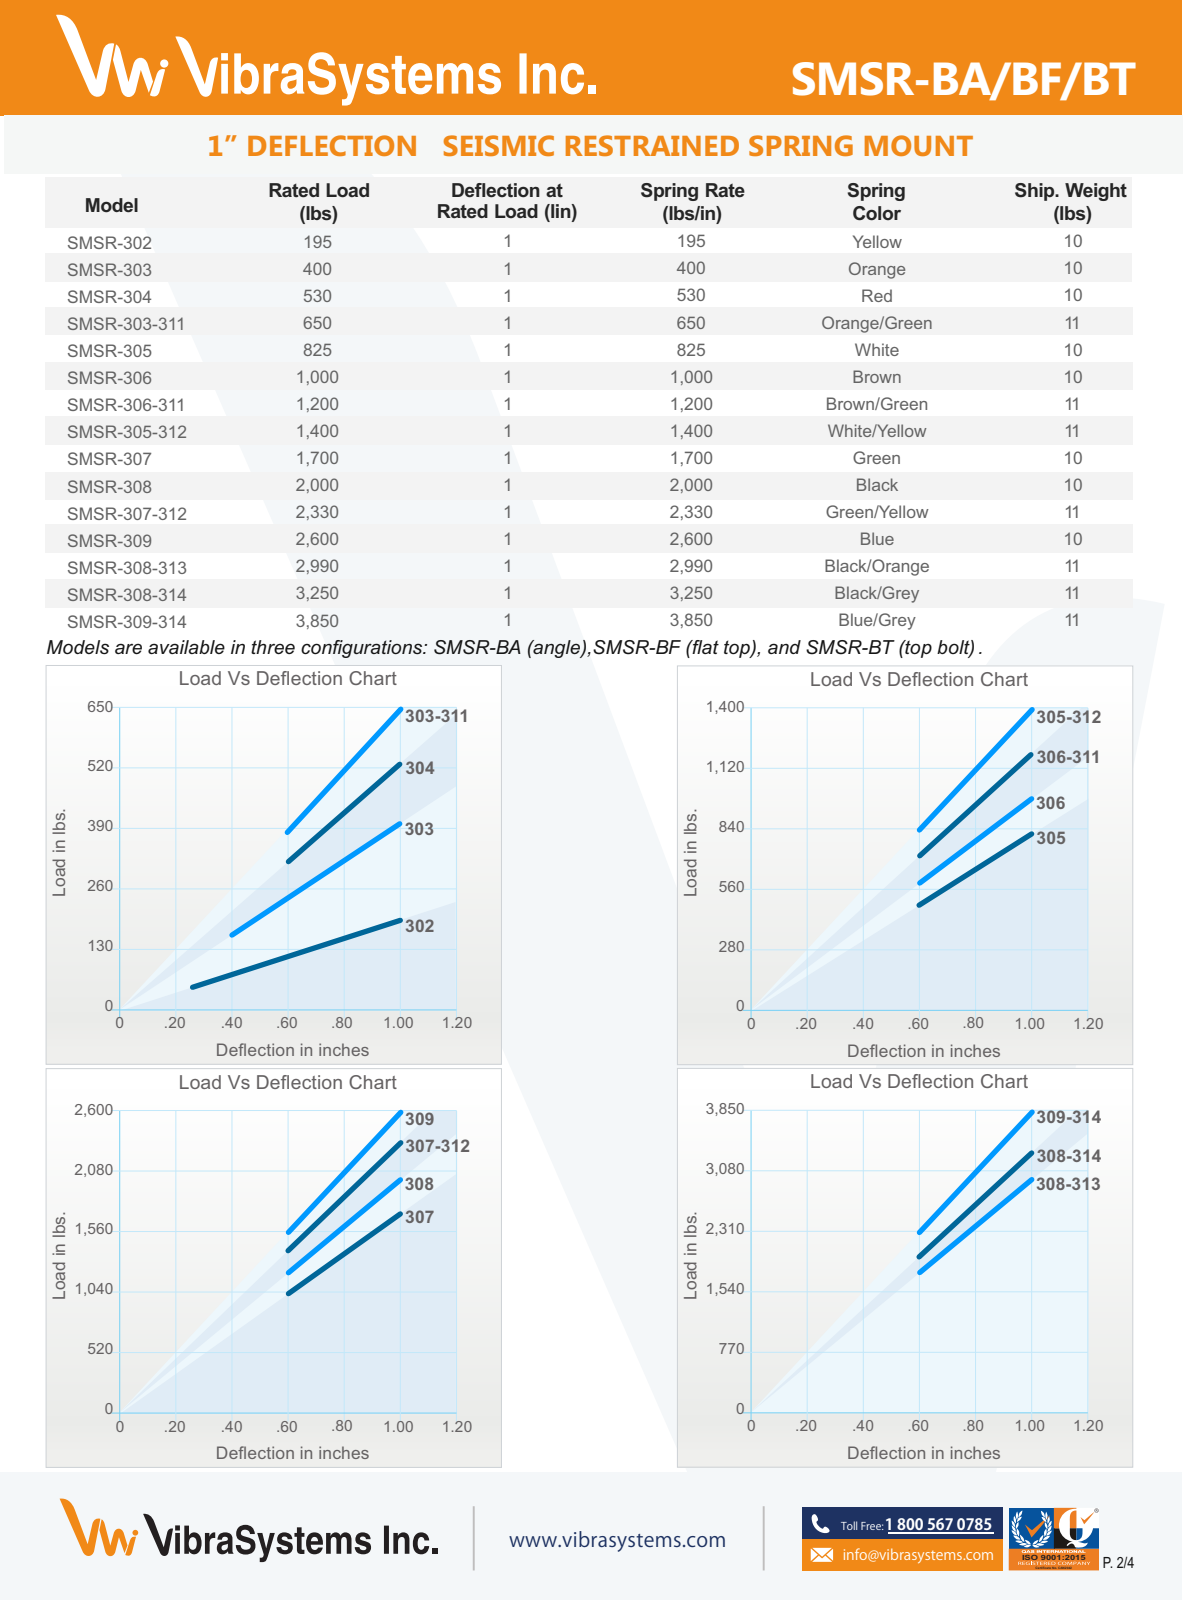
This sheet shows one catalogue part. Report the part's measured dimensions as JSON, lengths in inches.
{"part_name": "SMSR-BA Rev M", "step_written_by": "SolidWorks 2016 (CONFIG_CONTROL_DESIGN)", "units": "inches", "bodies": {"solids": 1, "faces": 121, "planar": 61, "cylindrical": 52, "other": 8}, "overall_size": [10.5, 7.5, 3.875], "volume_in3": 69.75, "surface_area_in2": 282.5, "round_holes": [[0.687, 3]], "round_bosses_or_shafts": [[0.5, 3], [1.5, 2], [1.4, 2], [3.5, 1], [3, 1], [1.375, 1]], "partial_cylinders_radius": [[0.25, 10], [0.062, 2], [0.188, 2], [0.5, 2], [0.563, 2], [0.187, 1], [0.375, 1]], "face_to_face_distances": [0.313, 3.937, 0.312, 1.5, 3.687, 5.687, 4.25, 3.625, 6, 0.187], "hole_center_spacings": [4.5, 9]}
